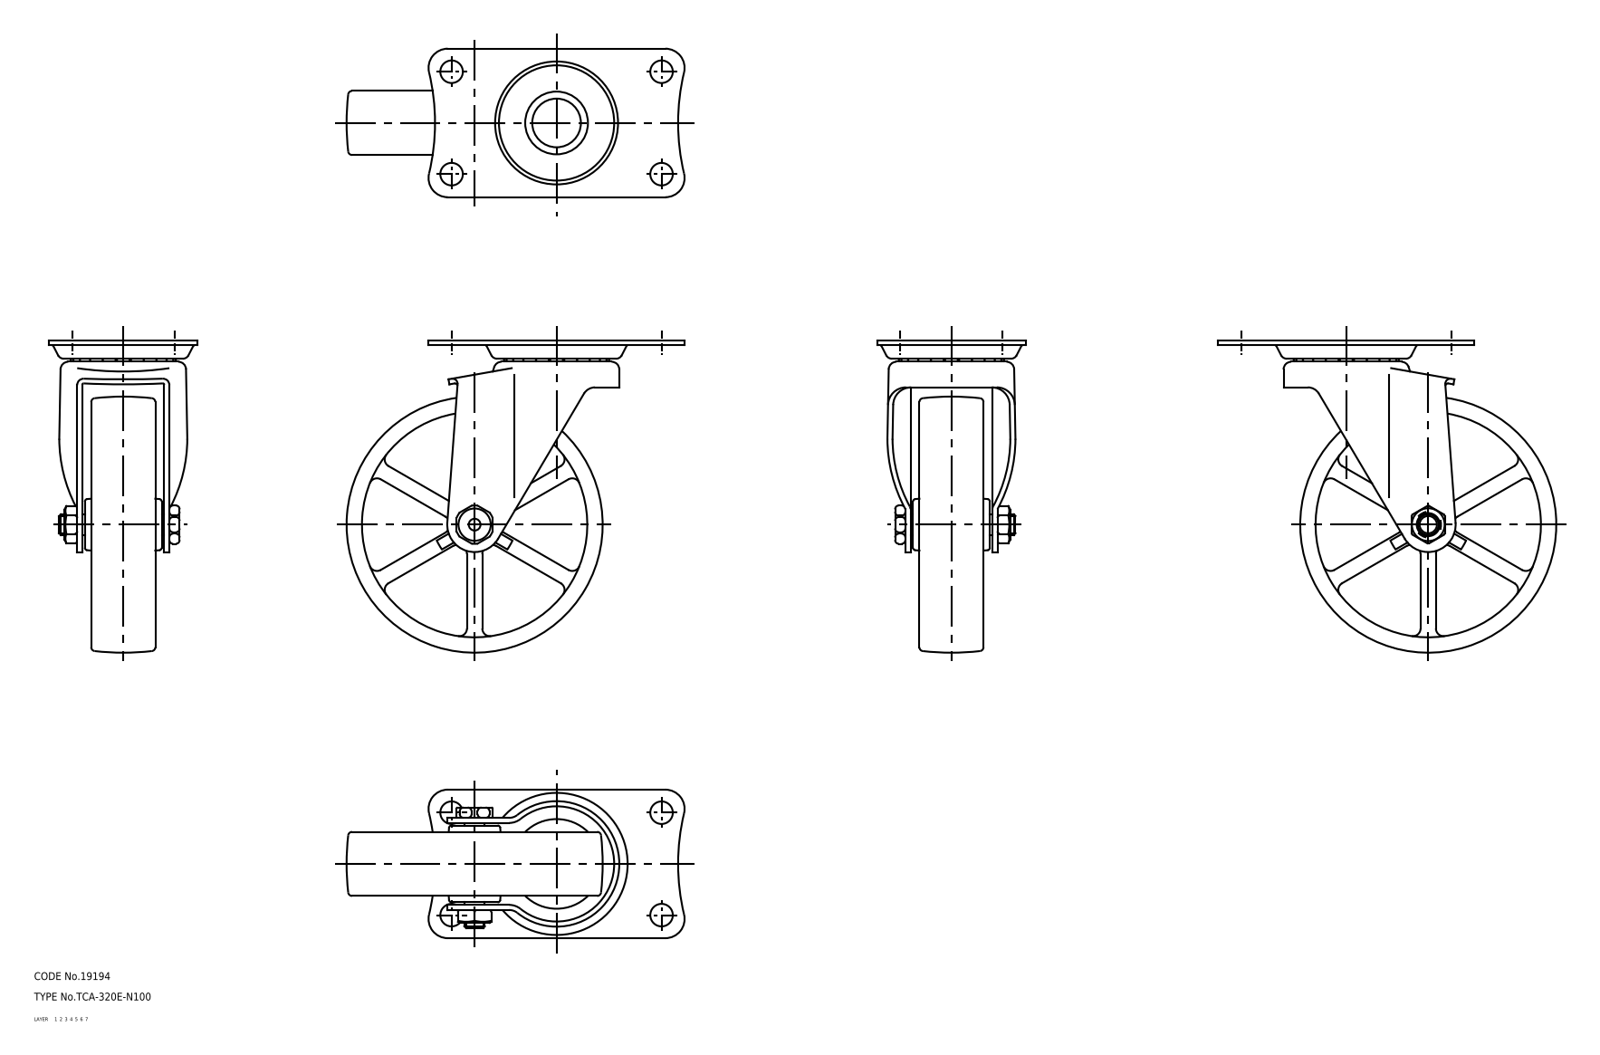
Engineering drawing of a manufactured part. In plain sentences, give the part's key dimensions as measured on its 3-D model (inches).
The part is named "wheel; mounting plate; main shaft; axle (+1 more)". Its 3-D file was written by "CADfix (AUTOMOTIVE_DESIGN)". It is 5 solids with 641 faces: 0 planar, 0 cylindrical and 641 other. Overall it measures 5.197 by 4.803 by 2.283 inches. Its volume is 11.2 cubic inches and its surface area 98.03 square inches.
